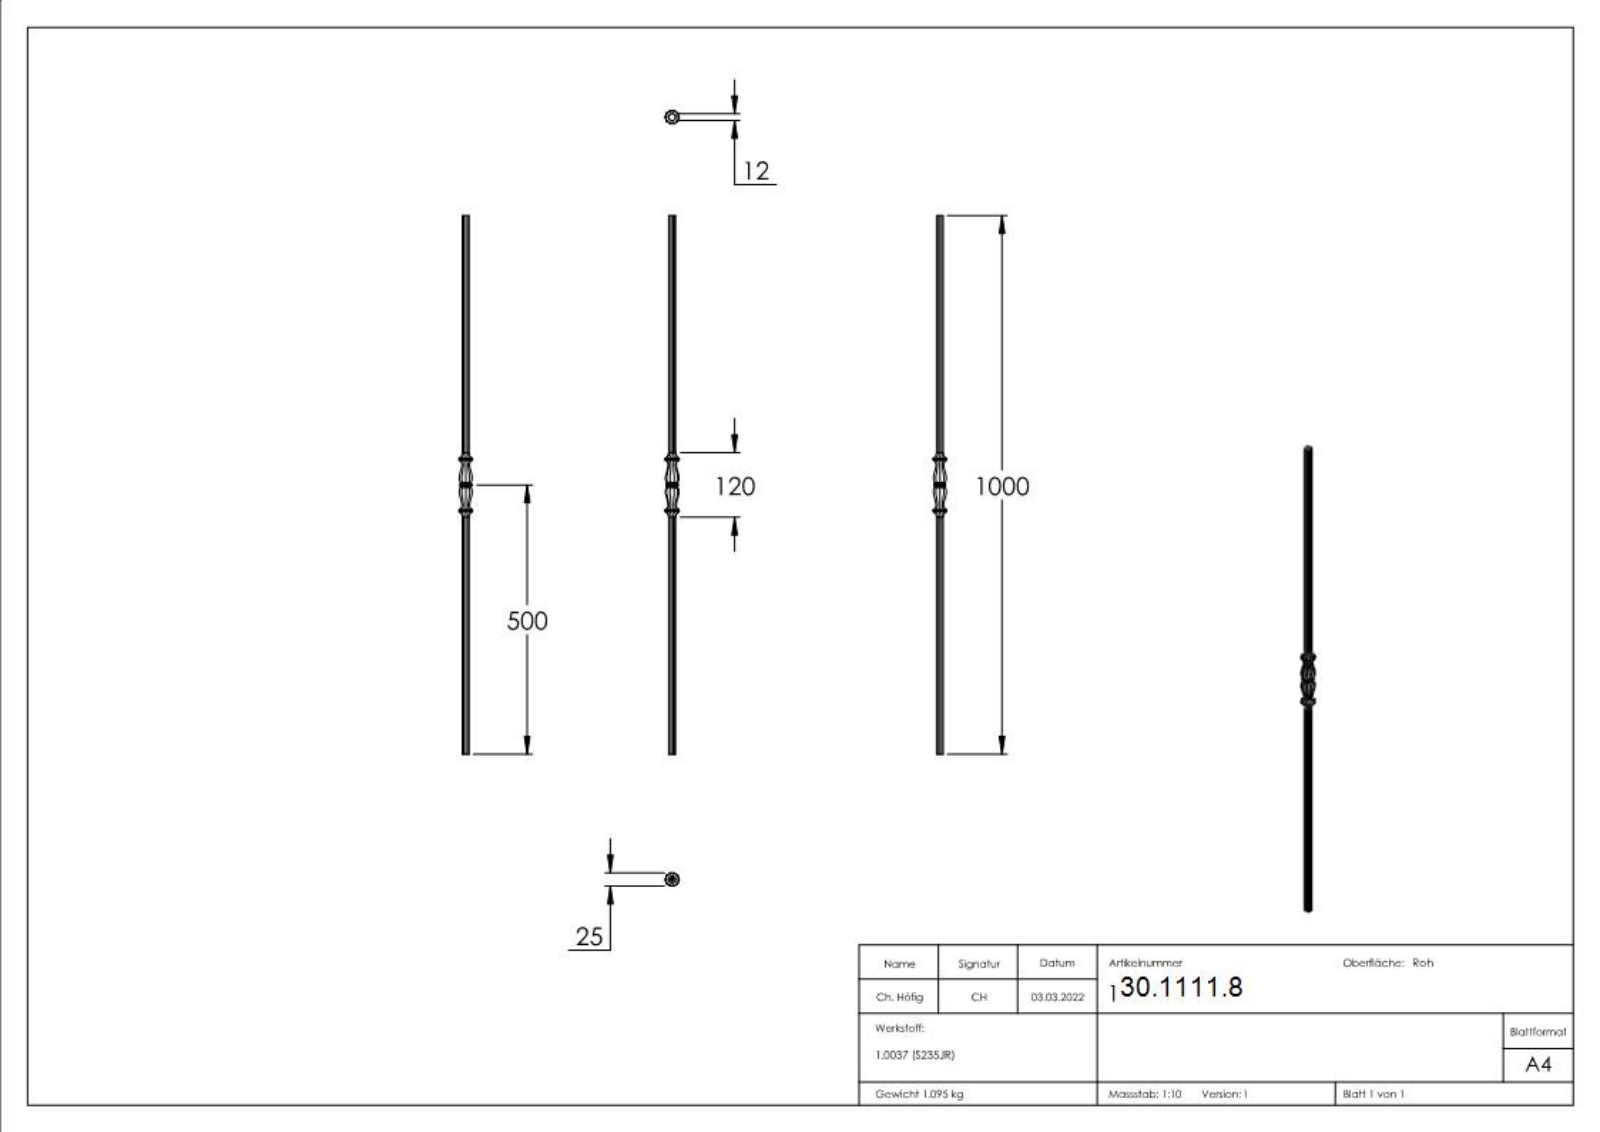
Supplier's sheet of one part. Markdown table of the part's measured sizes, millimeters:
| quantity | value |
| --- | --- |
| part name | 1872 |
| STEP written by | SolidWorks 2018 (CONFIG_CONTROL_DESIGN) |
| units | millimeters |
| bodies | 1 solid, 375 faces (164 planar, 20 cylindrical, 191 other) |
| overall size | 1000 × 26.29 × 25 |
| volume | 140 428 mm³ |
| surface area | 42 754 mm² |
| partial cylindrical surfaces (radius × count) | 3.75 × 20 |
| main face-to-face distances | 12, 6.5, 18.5, 2, 23, 4.5, 16.5, 25, 1000, 21 |
